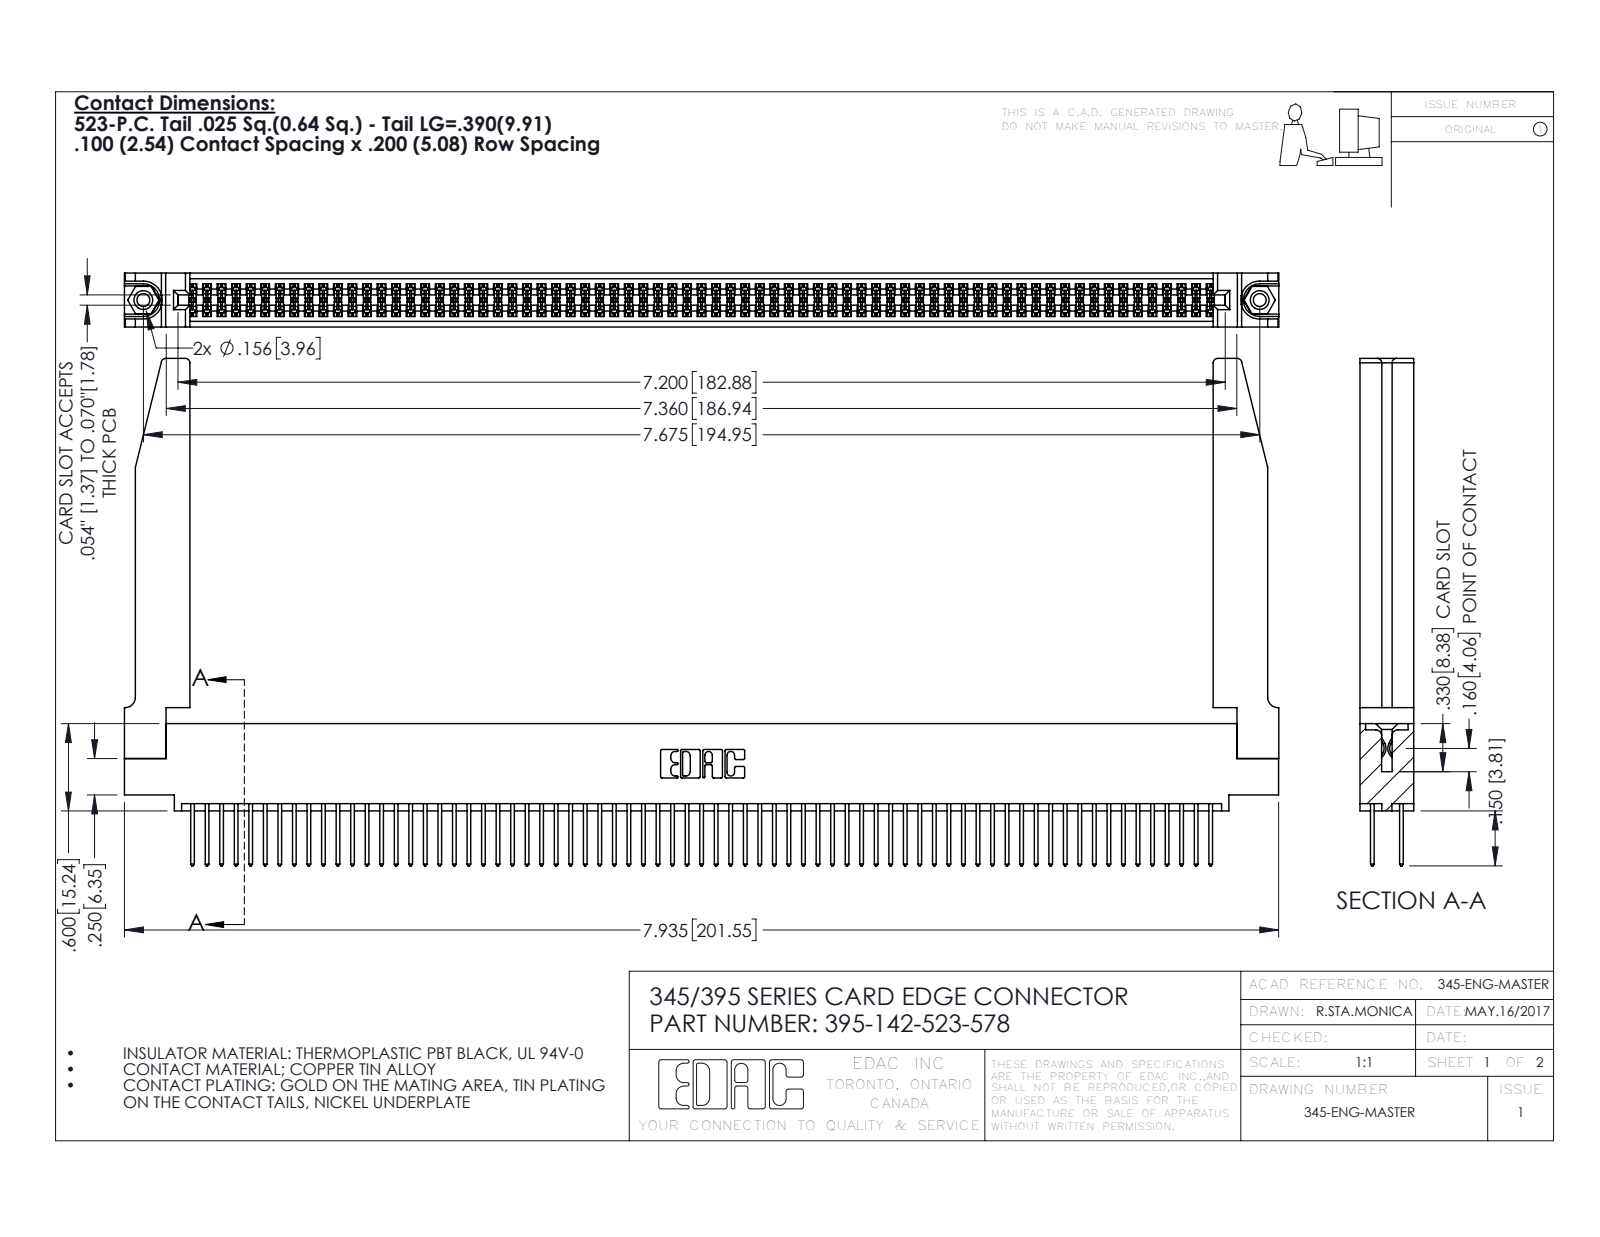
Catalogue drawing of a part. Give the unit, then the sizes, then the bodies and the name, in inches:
Units: inches
Overall size (bounding box): 7.936 × 3.487 × 0.37
Round holes (diameter × count): ⌀0.089 ×2, ⌀0.125 ×2, ⌀0.156 ×2, ⌀0.064 ×1
Round bosses / shafts (diameter × count): ⌀0.155 ×2
Partial cylindrical surfaces — rounded edges, fillets, slot ends (radius × count): R0.006 ×213, R0.01 ×142, R0.01 ×22, R0.03 ×8, R0.007 ×6, R0.031 ×6, R0.026 ×3, R0.014 ×2
Main face-to-face distances: 0.072, 0.298, 0.37, 0.098, 0.272, 0.025, 0.2, 0.225, 0.175, 0.149
Hole centre spacings: 0.27, 7.439, 7.675
Volume: 1.699 in³ · Surface area: 59.62 in²
Bodies: 147 solids, 7464 faces (4912 planar, 2500 cylindrical, 52 other)
Part name (STEP PRODUCT): 345-250-001_345-250-001-102; 345 Part_0.110 Offset - 0.156 Dia-TH; 345-292-001_345-293-123; 395-142-523-578 (+1 more)
STEP written by: SolidWorks 2016 (CONFIG_CONTROL_DESIGN)
